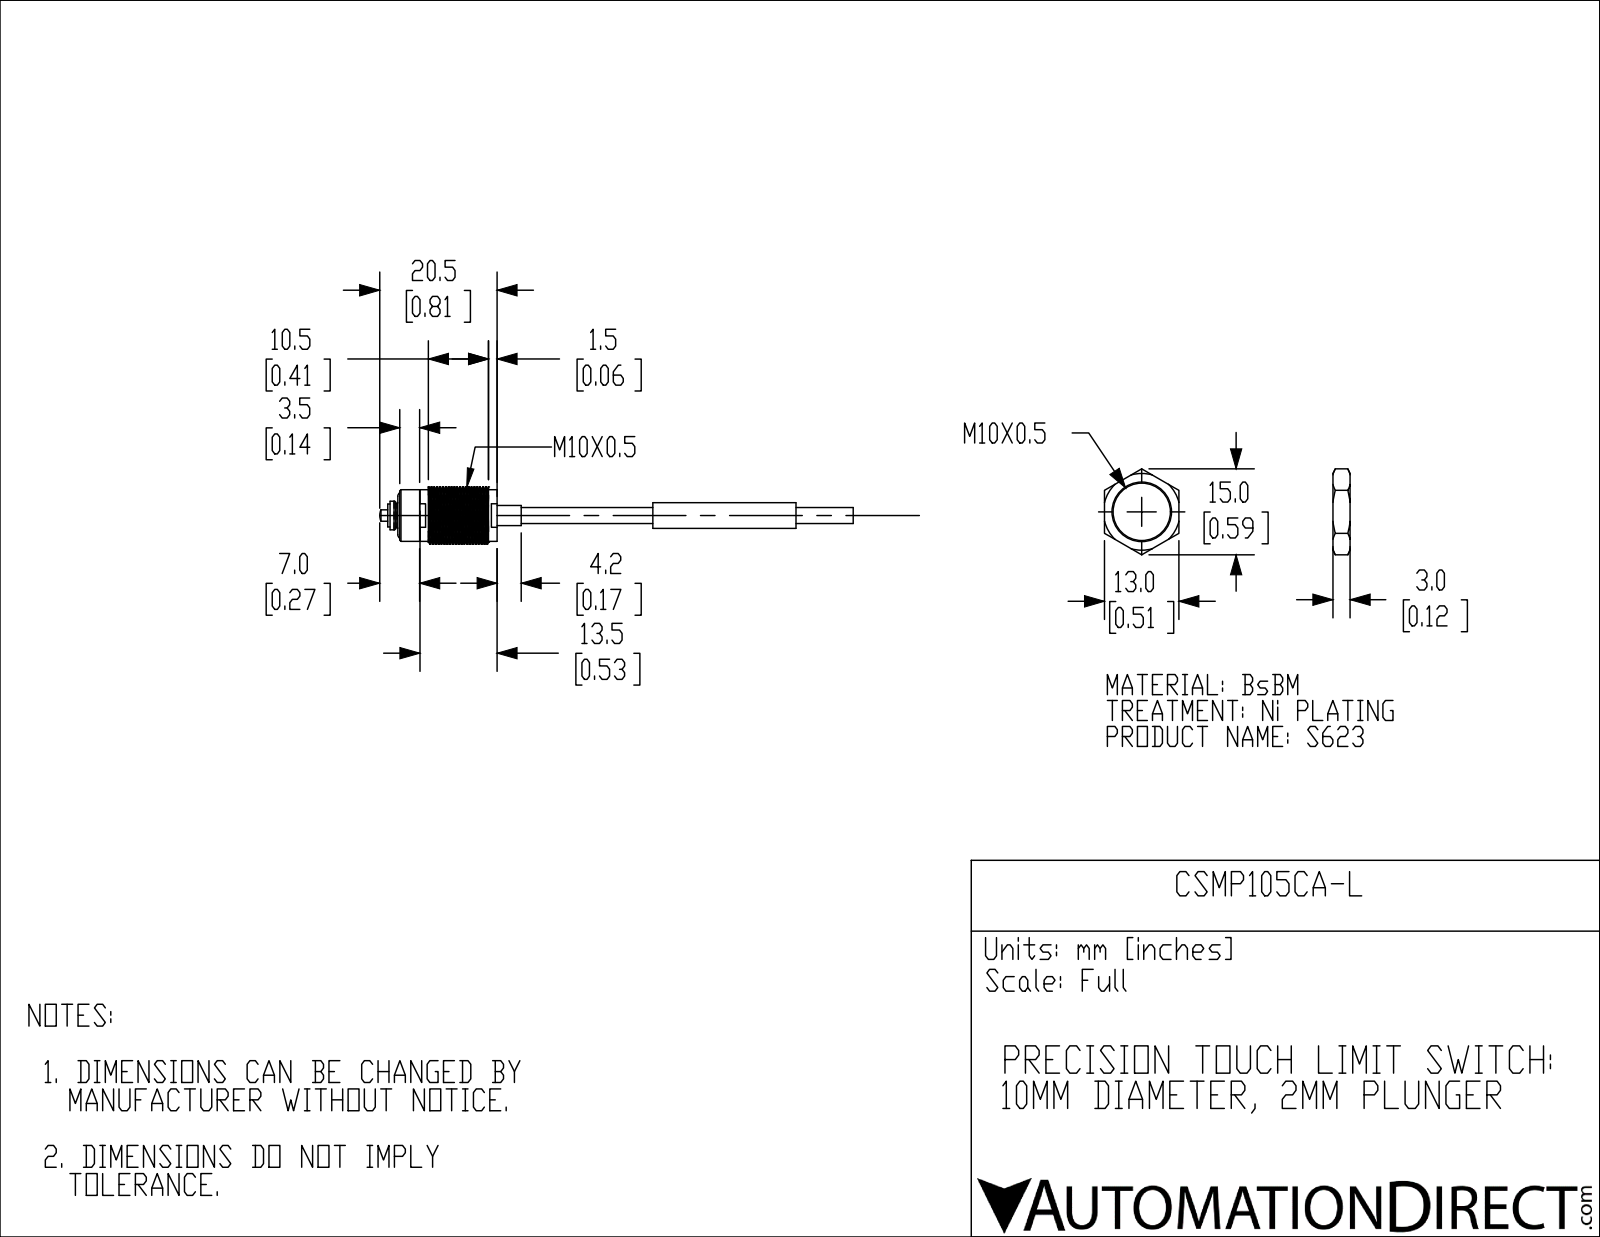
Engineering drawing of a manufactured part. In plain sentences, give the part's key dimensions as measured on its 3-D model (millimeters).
The part is named "CSMP105CA-L". Its 3-D file was written by "SolidWorks 2018 (AUTOMOTIVE_DESIGN)". It is 1 solid with 44 faces: 22 planar, 11 cylindrical and 11 other. Overall it measures 82.7 by 10 by 10 millimeters. Its volume is 1 920 cubic millimeters and its surface area 1 423 square millimeters. Round bosses or shafts: 1 of diameter 10, 1 of diameter 9, 1 of diameter 5, 1 of diameter 4.5, 1 of diameter 4, 1 of diameter 3.5, 1 of diameter 2.8, 1 of diameter 2. The main face-to-face distances are 17.3, 12, 1.5, 5.4, 15.8, 10.5, 0.4, 44.6, 69.5, 39.2.
